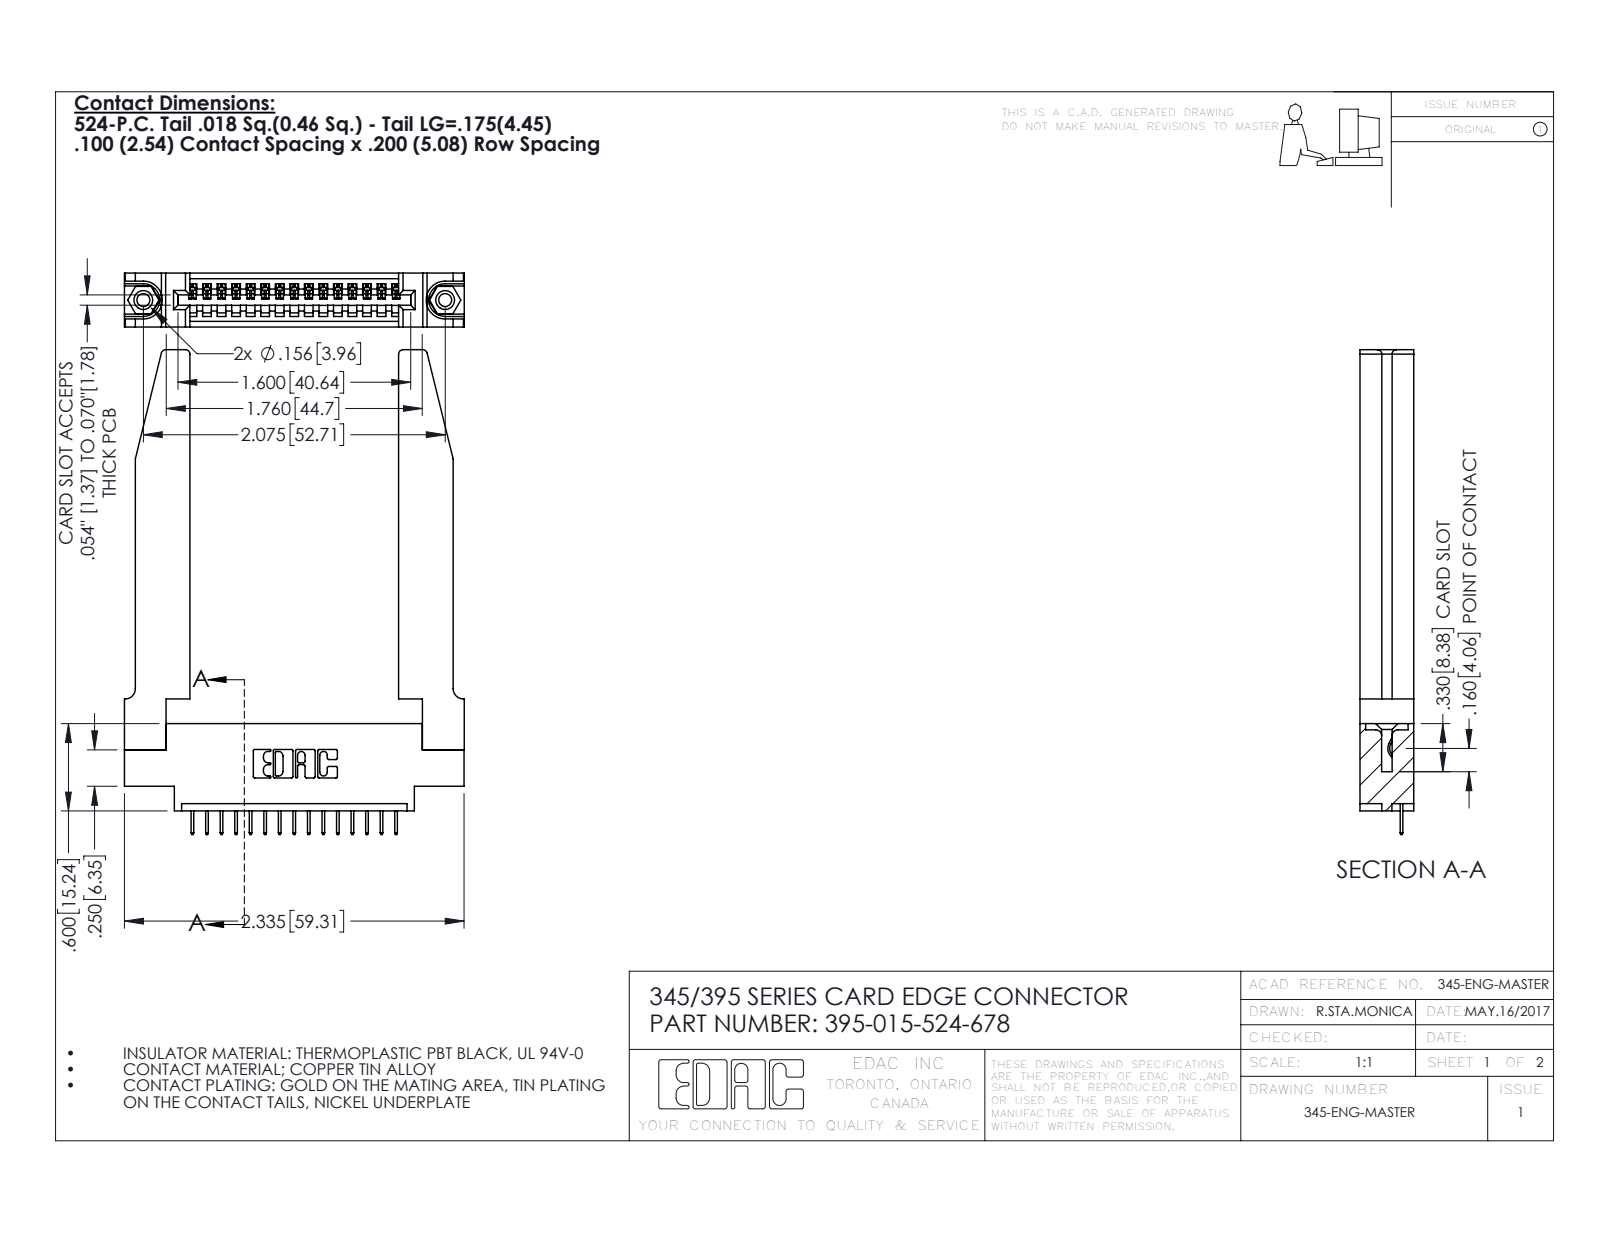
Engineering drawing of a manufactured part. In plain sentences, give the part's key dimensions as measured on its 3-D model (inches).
The part is named "345-292-001_345-293-124; 345-220-078_345-220-078; 345 Part_0.170 Offset - 0.156 Dia-TH; 395-015-524-678 (+1 more)". Its 3-D file was written by "SolidWorks 2016 (CONFIG_CONTROL_DESIGN)". It is 20 solids with 1294 faces: 916 planar, 326 cylindrical and 52 other. Overall it measures 3.332 by 2.336 by 0.37 inches. Its volume is 0.794 cubic inches and its surface area 20.74 square inches. Round holes: 2 of diameter 0.089, 2 of diameter 0.125, 2 of diameter 0.156, 1 of diameter 0.064. Round bosses or shafts: 2 of diameter 0.155. Partial cylindrical surfaces (rounded edges, fillets, slot ends): 30 of radius 0.006, 22 of radius 0.01, 8 of radius 0.03, 6 of radius 0.007, 6 of radius 0.031, 3 of radius 0.026, 2 of radius 0.031, 2 of radius 0.04. The main face-to-face distances are 0.37, 0.072, 0.298, 0.15, 0.148, 0.22, 0.077, 1.435, 0.123, 0.098. The hole center spacings are 0.27, 1.842, 2.075.
